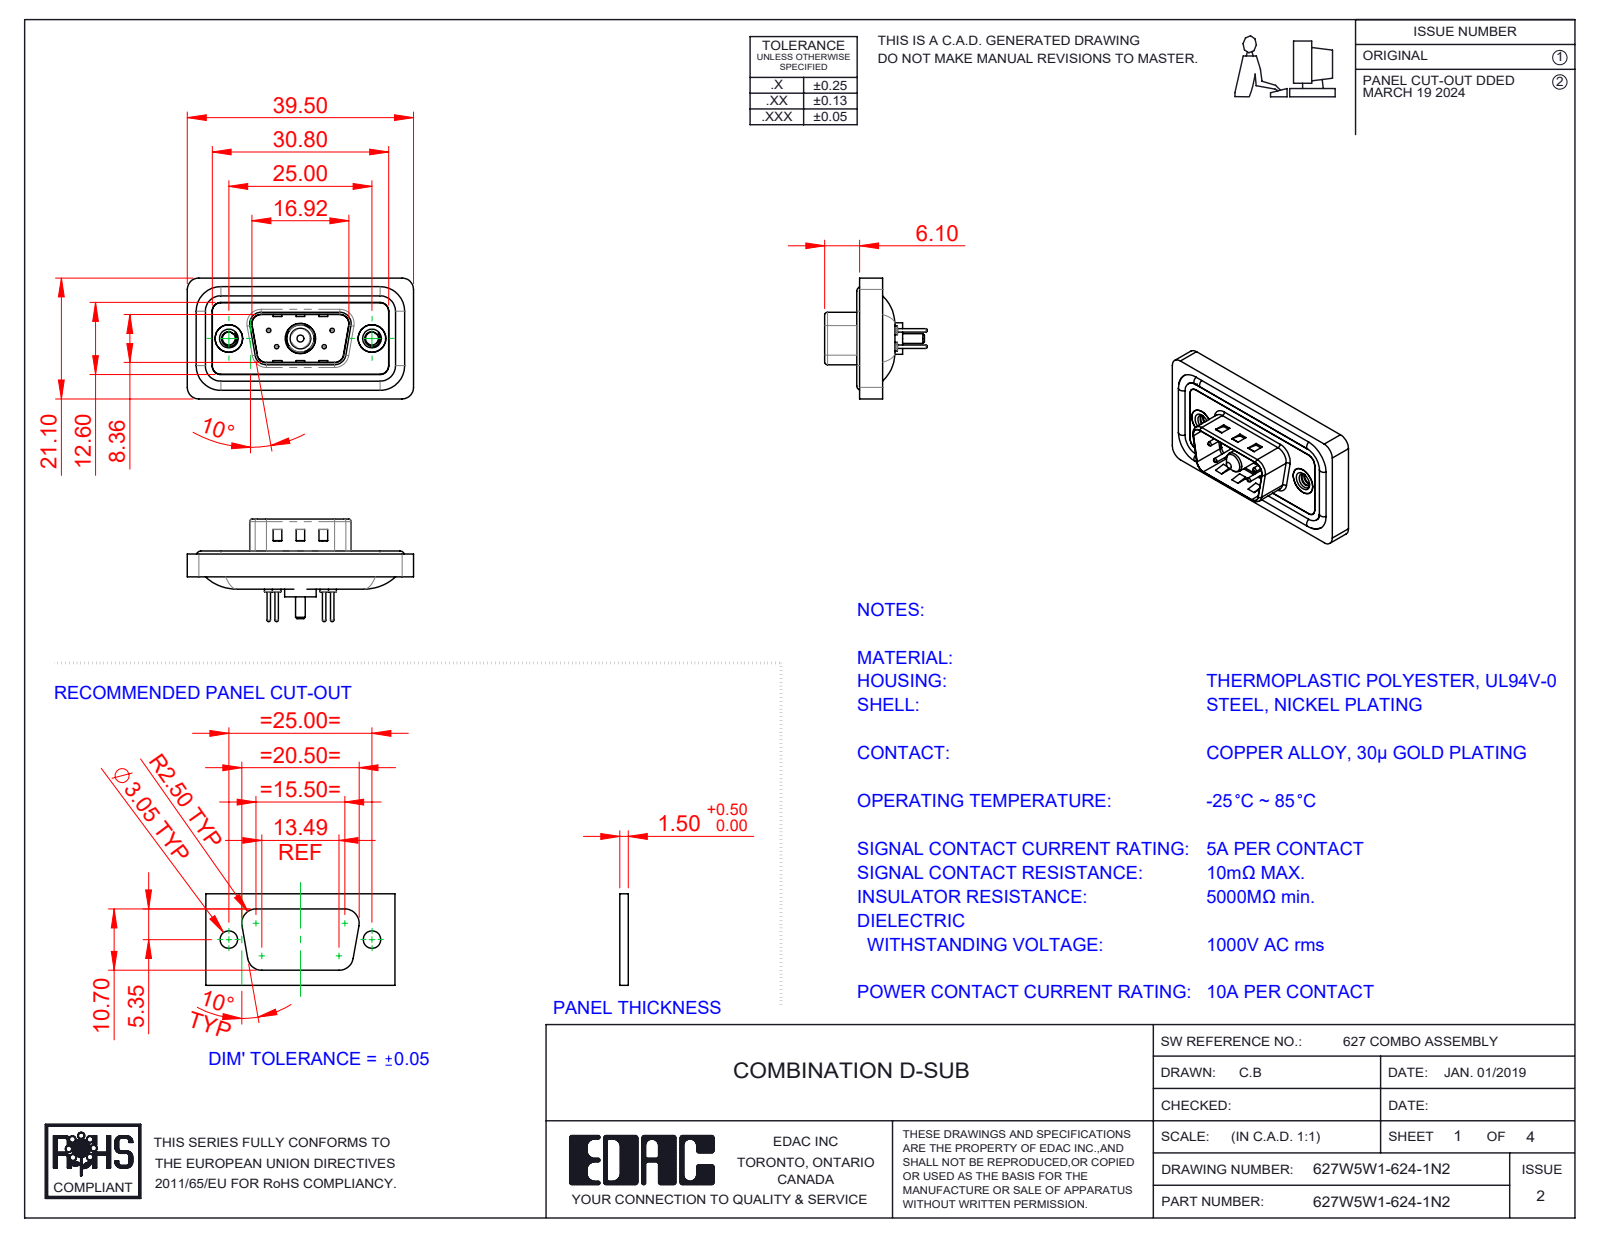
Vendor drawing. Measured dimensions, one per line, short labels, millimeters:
name: 627Combo Threaded Rivet_2; 627Combo Shell Rear_09 Contacts; 627Combo Contact Row 1_24; 627W5W1-624-1N2 (+5 more)
written by: SolidWorks 2023 (CONFIG_CONTROL_DESIGN)
unit: mm
bodies: 13 solids, 598 faces (183 planar, 255 cylindrical, 160 other)
size: 39.5 × 21.1 × 17.9
volume: 4 373 mm³; area: 6 929 mm²
holes: 4× ⌀0.75, 4× ⌀1.6, 4× ⌀2, 2× ⌀2.26, 2× ⌀4, 2× ⌀4.8, 2× ⌀5, 1× ⌀4.85, 1× ⌀5.3
bosses: 4× ⌀1.6, 4× ⌀1.5, 4× ⌀0.6, 2× ⌀4.9, 1× ⌀5.5, 1× ⌀5.2, 1× ⌀4.75, 1× ⌀3.75
rounds: 22× R1.5, 18× R2, 8× R0.5, 8× R1.6, 4× R0.25, 4× R0.6, 4× R0.65, 4× R0.9
face distances: 0.4, 1.1, 2.9, 1.6, 1.5, 3.1, 0.5, 2.5, 4, 0.8
hole spacings: 3.16, 5.72, 7.1, 12.5, 18.1, 4.39, 4.4, 8.31
